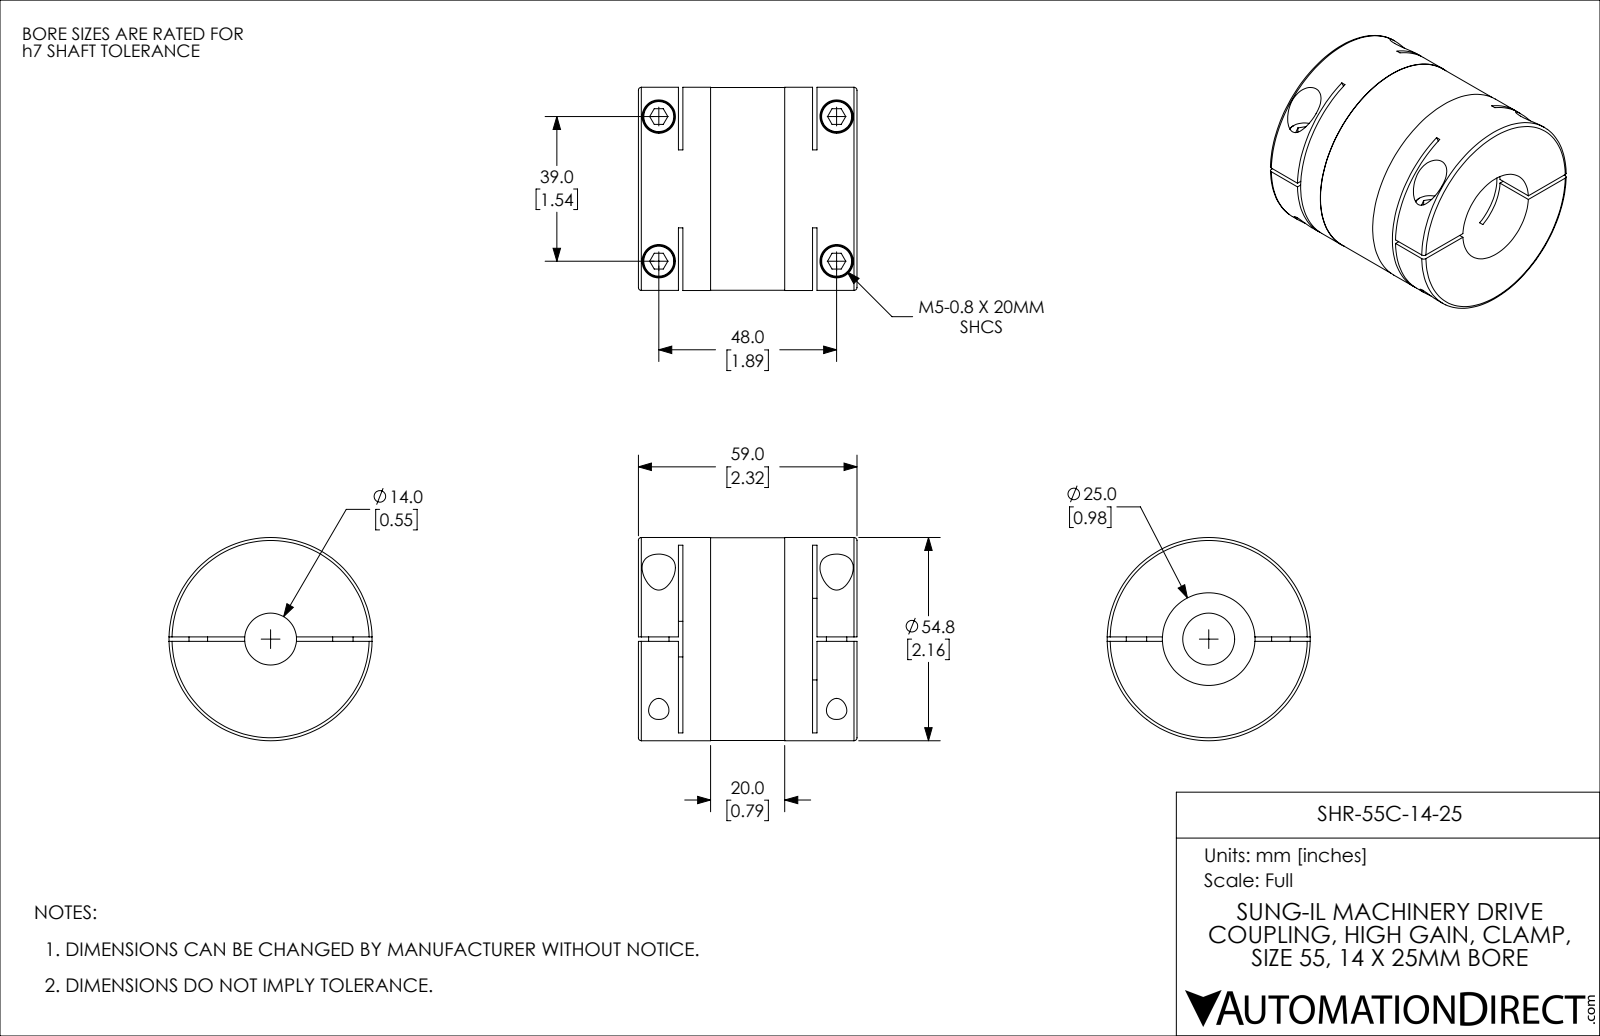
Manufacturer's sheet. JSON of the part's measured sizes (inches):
{"part_name": "SHR-55C-14-25", "step_written_by": "SolidWorks 2021 (CONFIG_CONTROL_DESIGN)", "units": "inches", "bodies": {"solids": 1, "faces": 144, "planar": 70, "cylindrical": 58, "other": 16}, "overall_size": [2.323, 2.157, 2.157], "volume_in3": 6.574, "surface_area_in2": 45.04, "round_holes": [[0.217, 4], [0.354, 4], [0.551, 1], [0.984, 1], [1.063, 1]], "round_bosses_or_shafts": [[0.335, 4], [0.197, 2], [2.157, 1], [2.154, 1]], "partial_cylinders_radius": [[2.362, 2]], "face_to_face_distances": [0.047, 0.472, 1.85, 0.425, 1.898, 1.425, 2.323, 1.378, 1.472, 0.768], "hole_center_spacings": [1.535, 1.89, 2.435]}
